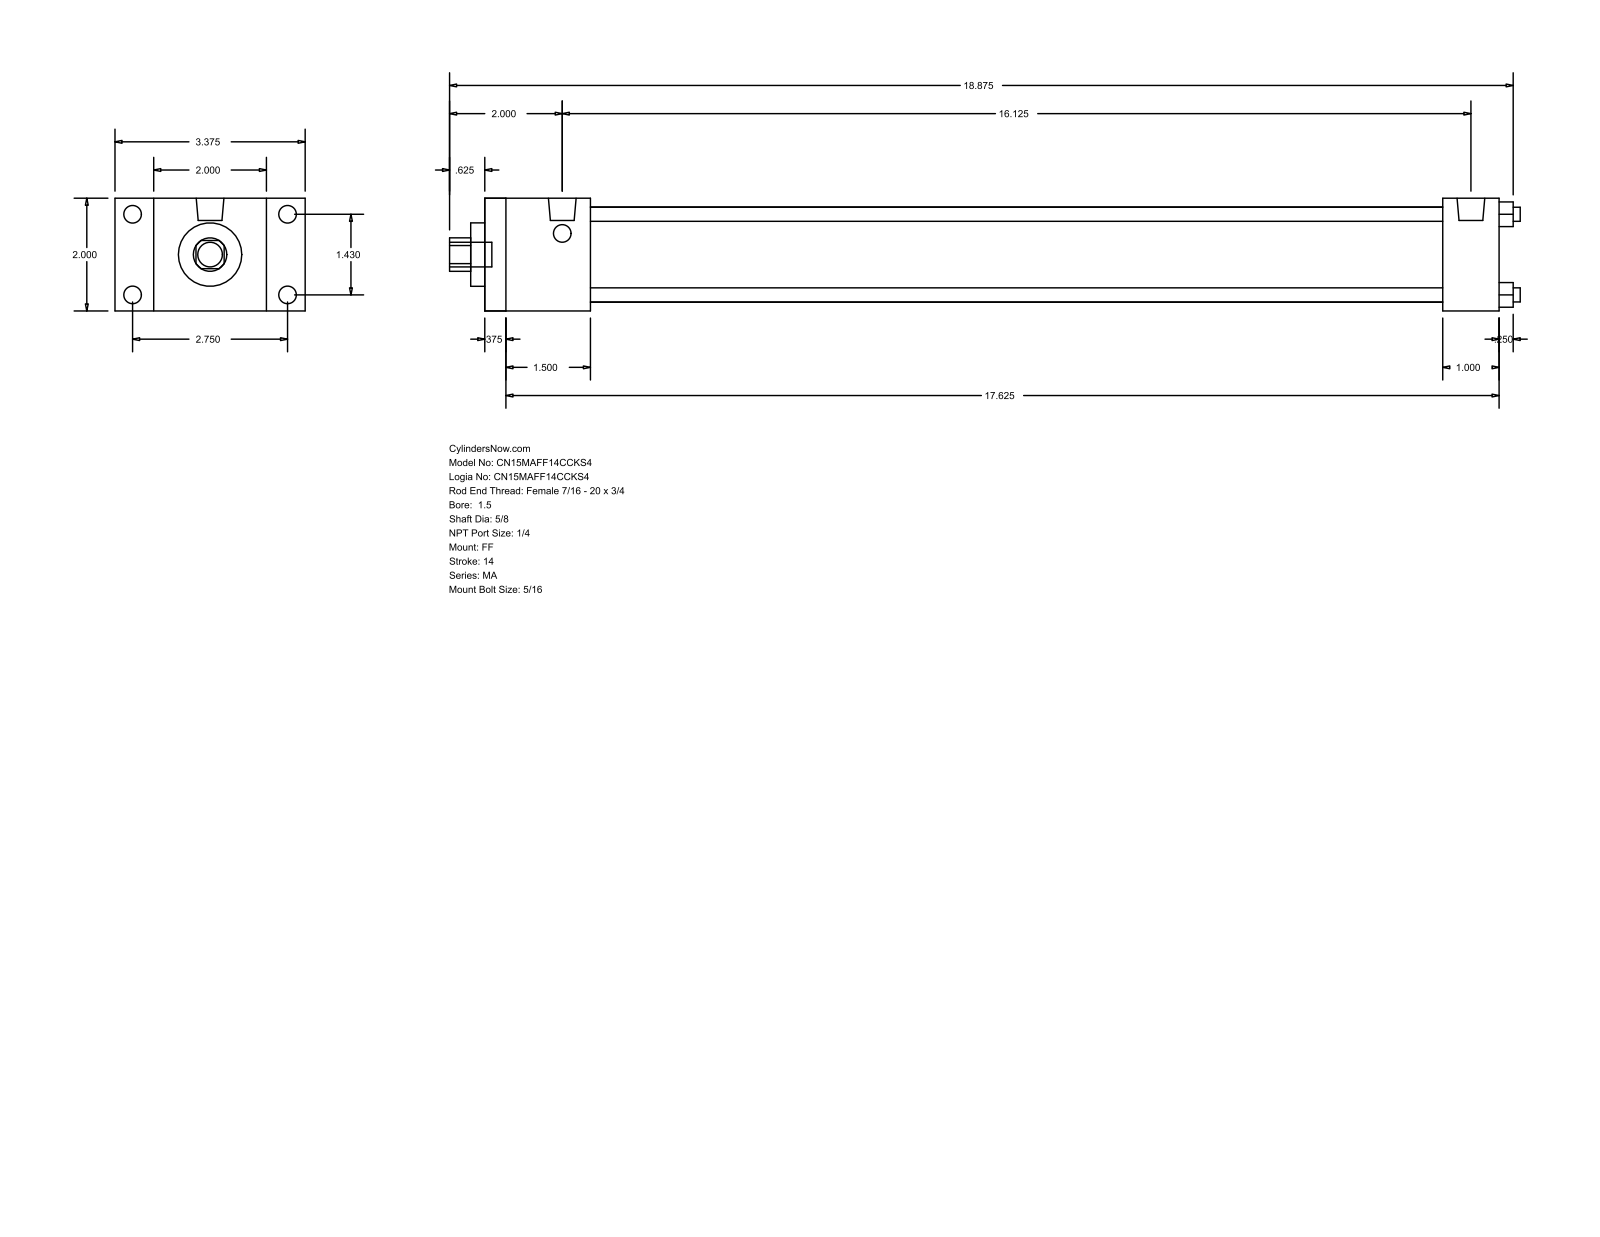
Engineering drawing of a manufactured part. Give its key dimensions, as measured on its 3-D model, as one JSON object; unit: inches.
{"part_name": "MA_FF__0150_0.625", "step_written_by": "GSSL Pune (CONFIG_CONTROL_DESIGN)", "units": "inches", "bodies": {"solids": 0, "faces": 92, "planar": 64, "cylindrical": 28, "other": 0}, "overall_size": [19, 3.375, 2], "round_holes": [[0.25, 4], [0.625, 1], [1.125, 1], [1.69, 1]], "round_bosses_or_shafts": [[0.313, 8], [0.492, 2], [0.437, 1]], "partial_cylinders_radius": [[0.297, 1]], "face_to_face_distances": [2, 18, 0.375, 17.625, 1.875, 17, 1.5, 16.625, 15.125, 16.125], "hole_center_spacings": [1.011, 1.43, 2.022]}
